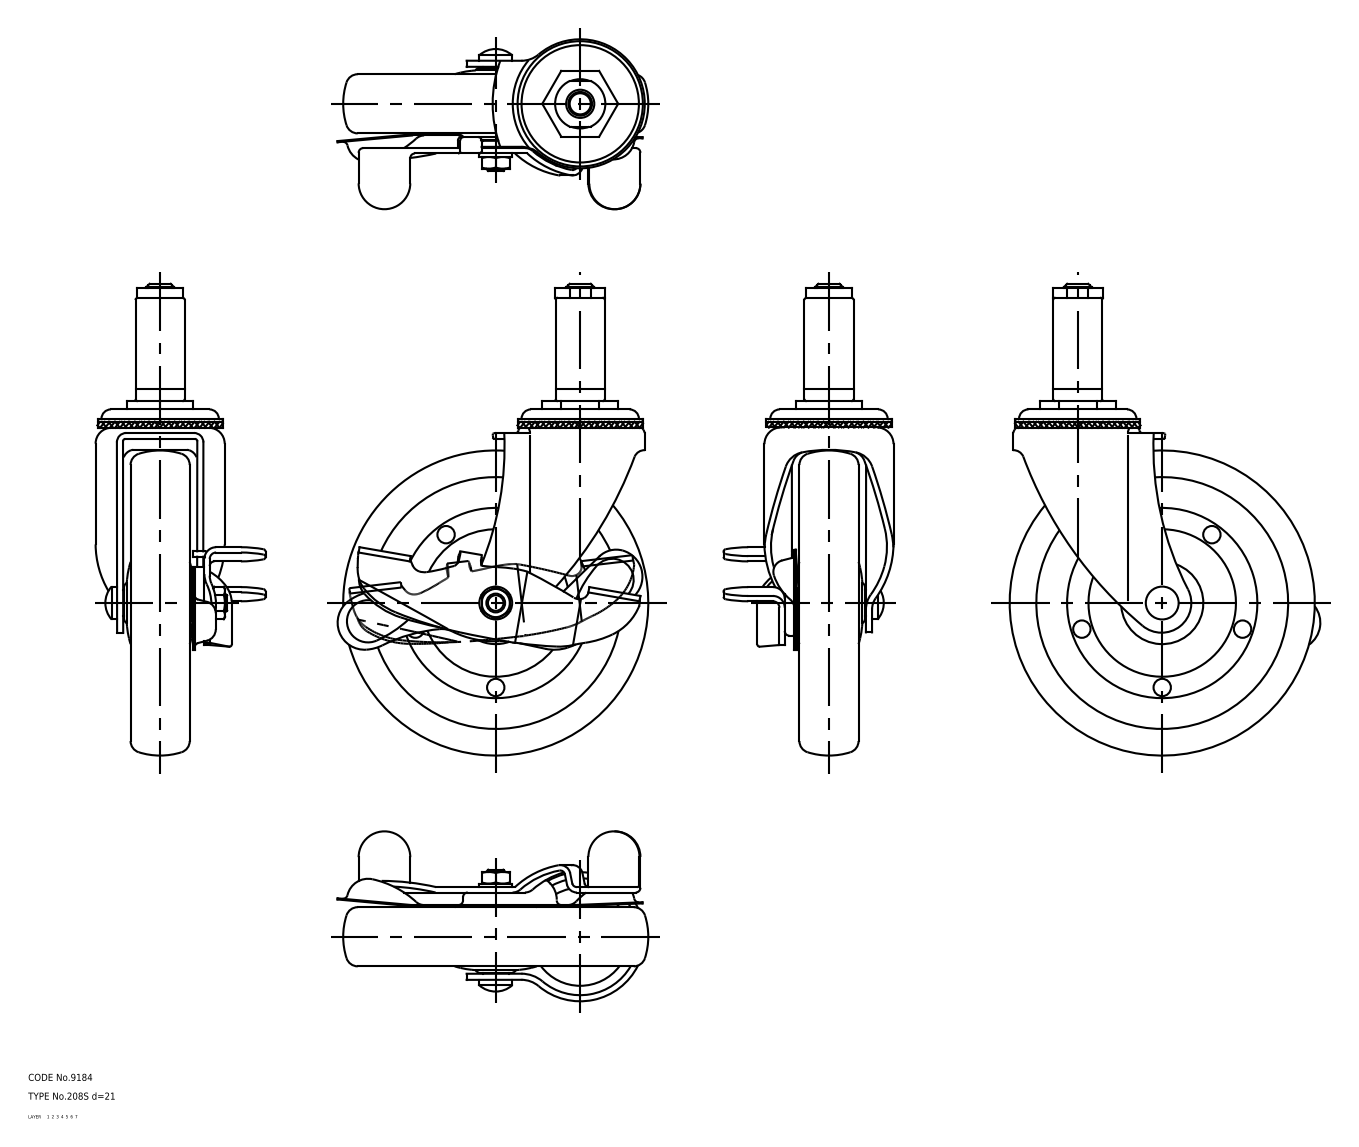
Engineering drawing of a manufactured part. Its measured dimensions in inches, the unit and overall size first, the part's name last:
Units: inches
Overall size (bounding box): 7.913 × 5.211 × 2.851
Volume: 19.66 in³ · Surface area: 136.6 in²
Bodies: 6 solids, 395 faces (0 planar, 0 cylindrical, 395 other)
Part name (STEP PRODUCT): lever; wheel; plate; main shaft (+2 more)
STEP written by: CADfix (AUTOMOTIVE_DESIGN)
